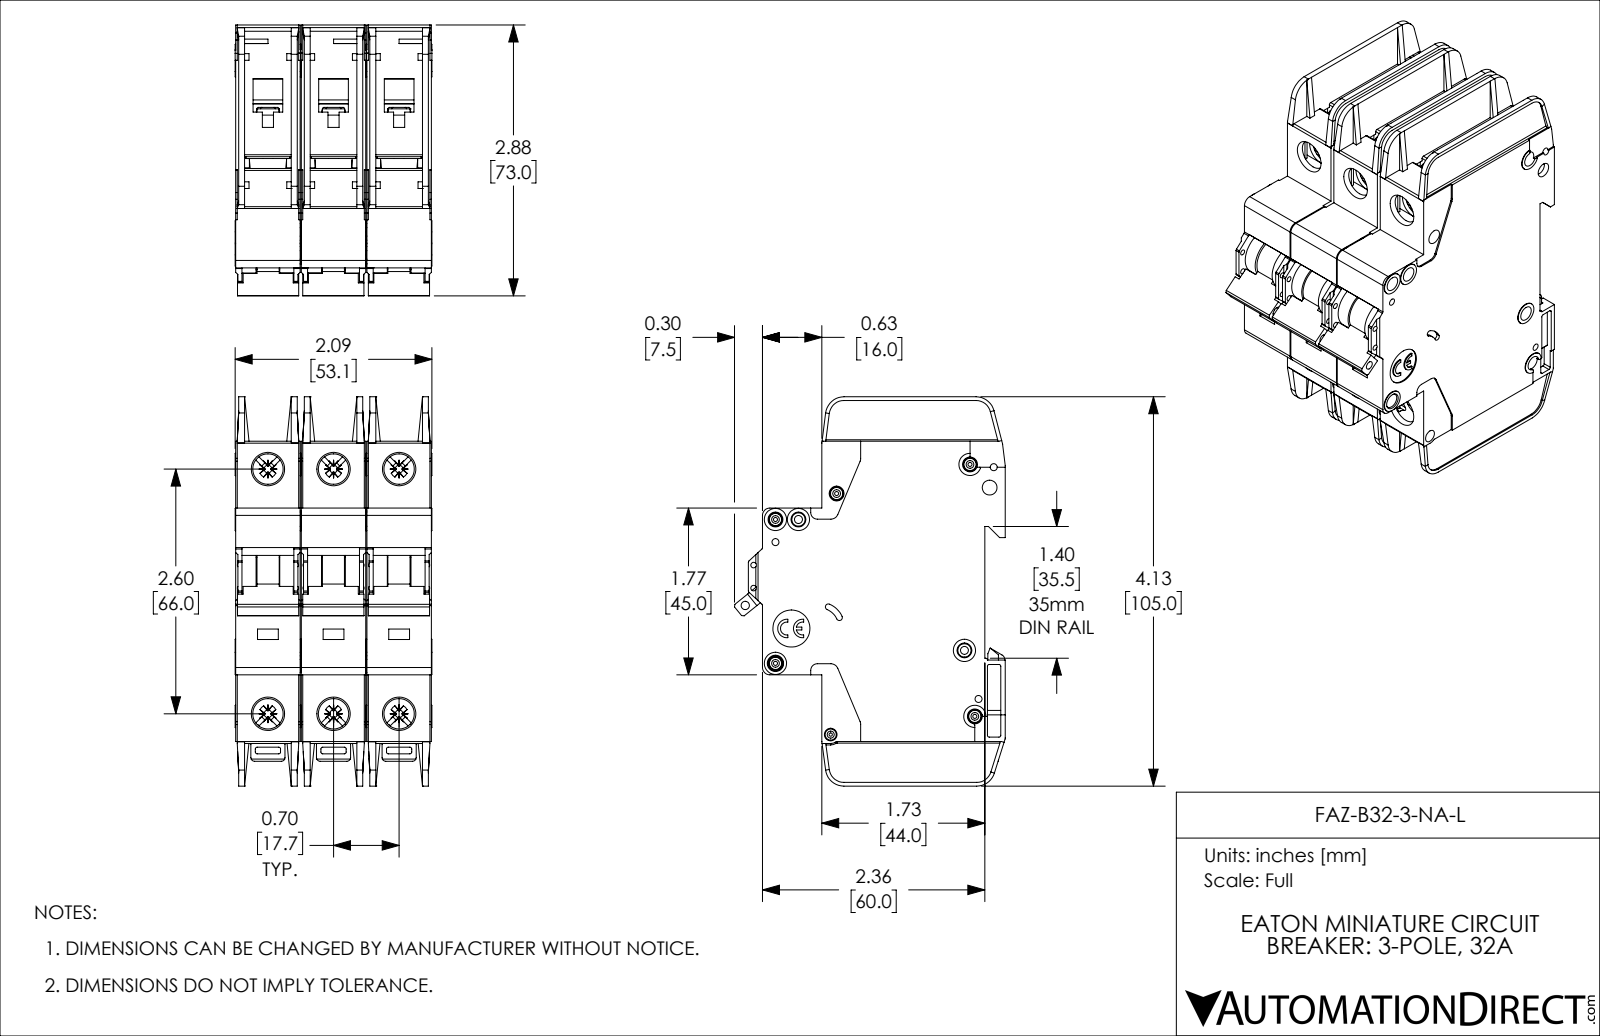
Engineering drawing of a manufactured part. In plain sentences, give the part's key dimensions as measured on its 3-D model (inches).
The part is named "FAZ-B32-3-NA-L". Its 3-D file was written by "SolidWorks 2019 (AUTOMOTIVE_DESIGN)". It is 3 solids with 3381 faces: 2013 planar, 1071 cylindrical and 297 other. Overall it measures 4.134 by 2.876 by 2.091 inches. Its volume is 14.05 cubic inches and its surface area 123 square inches. Round holes: 8 of diameter 0.157, 6 of diameter 0.323, 5 of diameter 0.043, 4 of diameter 0.075, 2 of diameter 0.059, 2 of diameter 0.085, 1 of diameter 0.035, 1 of diameter 0.089, 1 of diameter 0.098, 1 of diameter 0.134, 1 of diameter 0.394. Round bosses or shafts: 5 of diameter 0.13, 4 of diameter 0.236, 4 of diameter 0.118, 3 of diameter 0.098. Partial cylindrical surfaces (rounded edges, fillets, slot ends): 72 of radius 0.02, 30 of radius 0.016, 18 of radius 0.039, 12 of radius 0.043, 12 of radius 0.079, 6 of radius 0.008, 6 of radius 0.01, 6 of radius 0.028. The main face-to-face distances are 0.697, 0.047, 1.394, 0.685, 0.591, 1.382, 0.744, 0.65, 0.106, 0.094. The hole center spacings are 0.697, 2.69, 2.598, 0.244, 0.537, 0.87, 1.394, 2.948.
